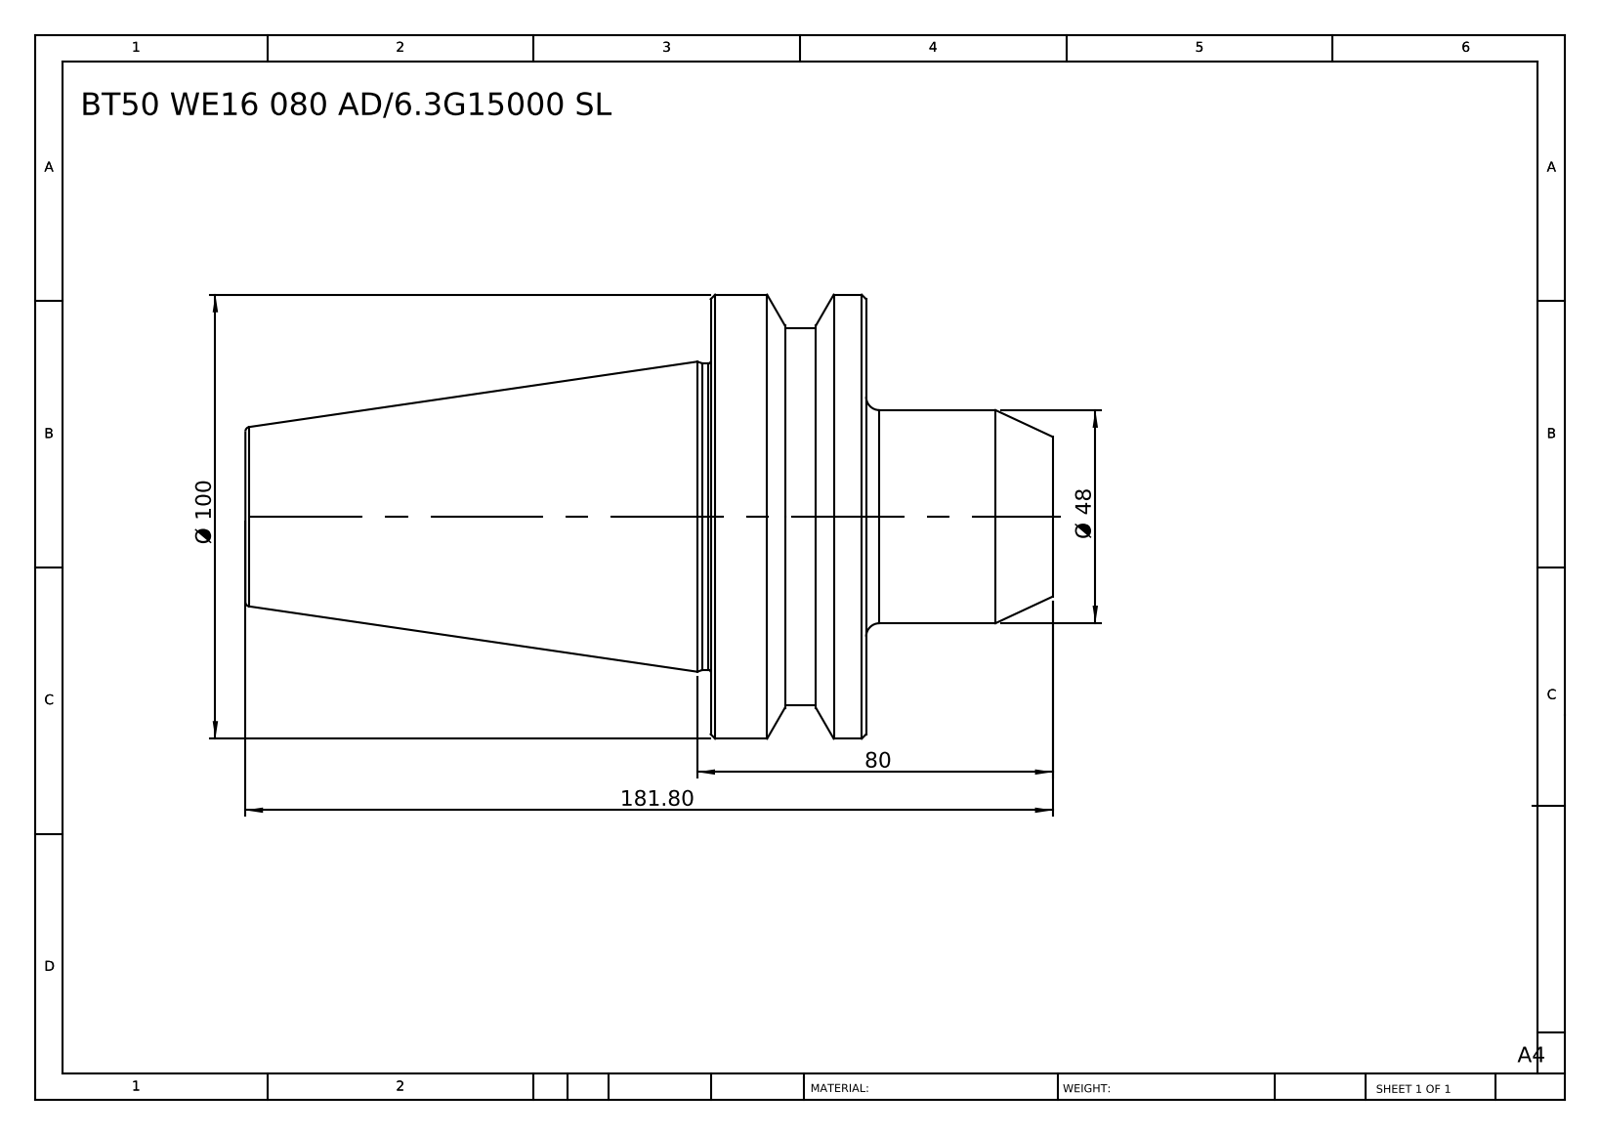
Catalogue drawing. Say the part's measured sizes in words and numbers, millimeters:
The part is named "BT50 WE16 080 AD-6.3G15000 SL". Its 3-D file was written by "SolidWorks 2014 (CONFIG_CONTROL_DESIGN)". It is 1 solid with 36 faces: 6 planar, 10 cylindrical and 20 other. Overall it measures 181.8 by 100 by 100 millimeters. Its volume is 581 025 cubic millimeters and its surface area 49 650 square millimeters. Round bosses or shafts: 1 of diameter 100, 1 of diameter 85, 1 of diameter 69, 1 of diameter 48. The main face-to-face distances are 35, 139.8, 104.8, 42, 77, 181.8, 53.3, 11.3, 23.7, 128.5.
